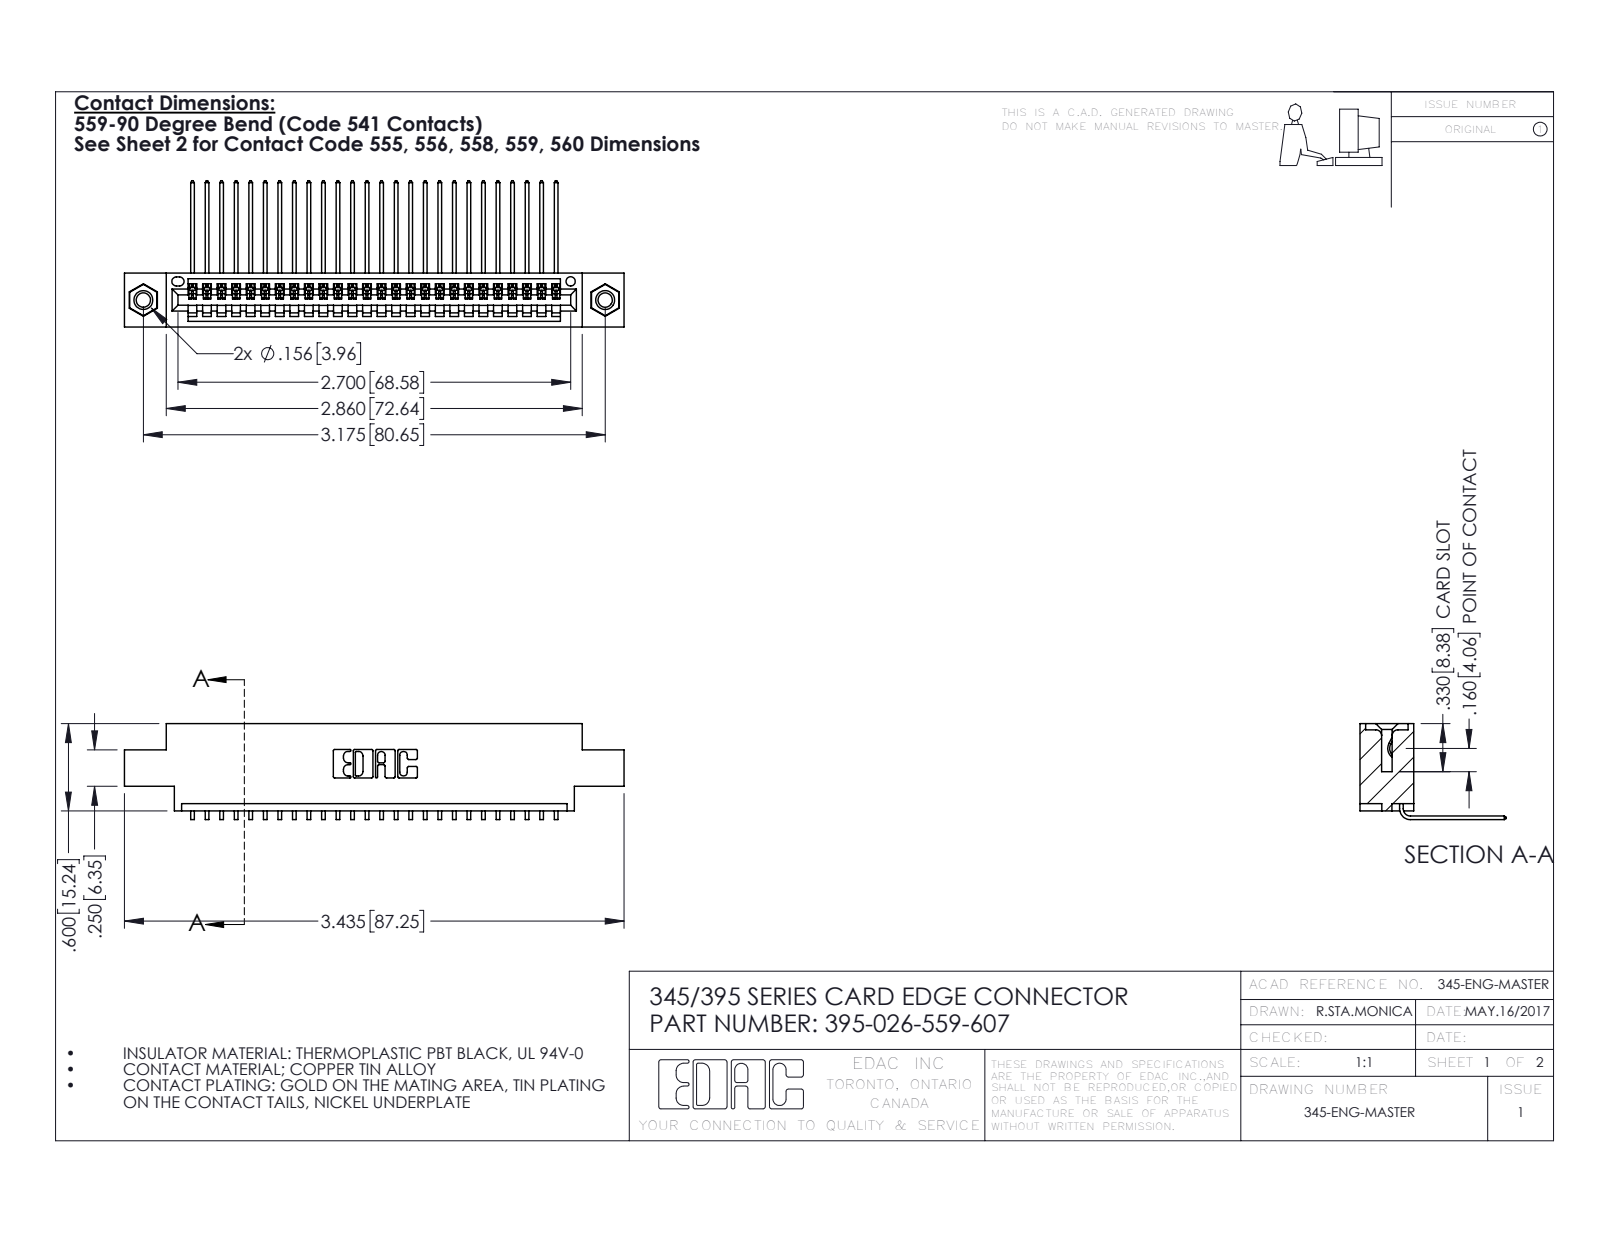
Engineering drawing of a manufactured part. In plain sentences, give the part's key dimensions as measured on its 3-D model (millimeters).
The part is named "345-250-001_345-250-005-103; 345 Part_0.170 Offset - 0.156 Dia-TI; 395-026-559-607; 345-292-001_558 559 Tail - 1". Its 3-D file was written by "SolidWorks 2016 (CONFIG_CONTROL_DESIGN)". It is 29 solids with 1750 faces: 1208 planar, 526 cylindrical and 16 other. Overall it measures 87.2 by 25.5 by 16.7 millimeters. Its volume is 8 110 cubic millimeters and its surface area 11 240 square millimeters. Round holes: 2 of diameter 2.5, 2 of diameter 3.2, 2 of diameter 4, 1 of diameter 1.6. Round bosses or shafts: 2 of diameter 3.9. Partial cylindrical surfaces (rounded edges, fillets, slot ends): 52 of radius 0.2, 22 of radius 0.3, 6 of radius 0.2, 6 of radius 0.8, 3 of radius 0.7, 2 of radius 0.8, 2 of radius 1, 1 of radius 0.4. The main face-to-face distances are 1.8, 7.6, 9.4, 5.1, 2.5, 6.9, 0.6, 5.7, 4.4, 3.8. The hole center spacings are 6.9, 74.7, 80.6.
